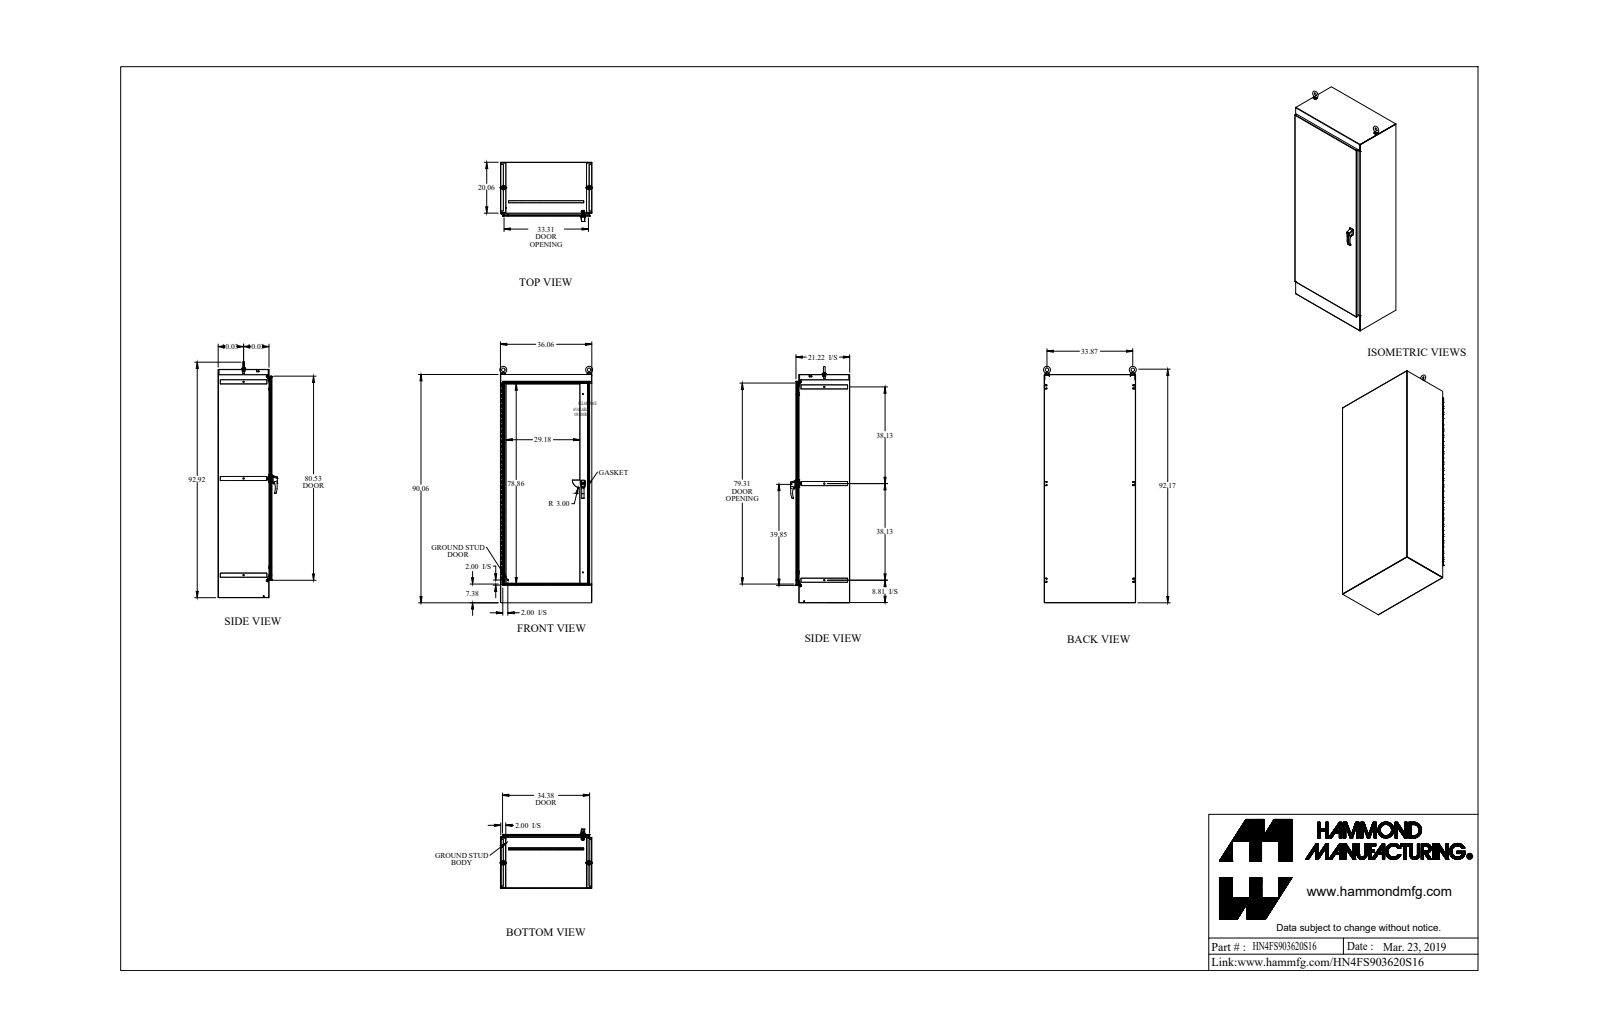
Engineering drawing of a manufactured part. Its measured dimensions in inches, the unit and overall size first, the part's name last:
Units: inches
Overall size (bounding box): 93.489 × 36.604 × 23.362
Round holes (diameter × count): ⌀0.304 ×13, ⌀0.35 ×7, ⌀0.5 ×3, ⌀0.25 ×2, ⌀0.257 ×2, ⌀0.28 ×2, ⌀0.281 ×2, ⌀0.313 ×2, ⌀0.39 ×2, ⌀0.413 ×2, ⌀0.527 ×2, ⌀0.68 ×2
Round bosses / shafts (diameter × count): ⌀1.75 ×2, ⌀1.5 ×2, ⌀1.25 ×2, ⌀1 ×2, ⌀0.75 ×2, ⌀0.738 ×2, ⌀0.63 ×2, ⌀0.625 ×2
Partial cylindrical surfaces — rounded edges, fillets, slot ends (radius × count): R0.043 ×42, R0.138 ×36, R0.5 ×23, R0.125 ×22, R0.018 ×16, R0.06 ×15, R0.048 ×13, R0.143 ×13
Main face-to-face distances: 0.095, 21.152, 35.965, 21.057, 21.247, 35.87, 36.06, 89.965, 19.965, 1.187
Hole centre spacings: 6, 12, 18, 24, 30, 36, 42, 48
Volume: 1 292 in³ · Surface area: 27 271 in²
Bodies: 57 solids, 2060 faces (940 planar, 955 cylindrical, 165 other)
Part name (STEP PRODUCT): HN4FS903620S16
STEP written by: SolidWorks 2018 (AUTOMOTIVE_DESIGN)
